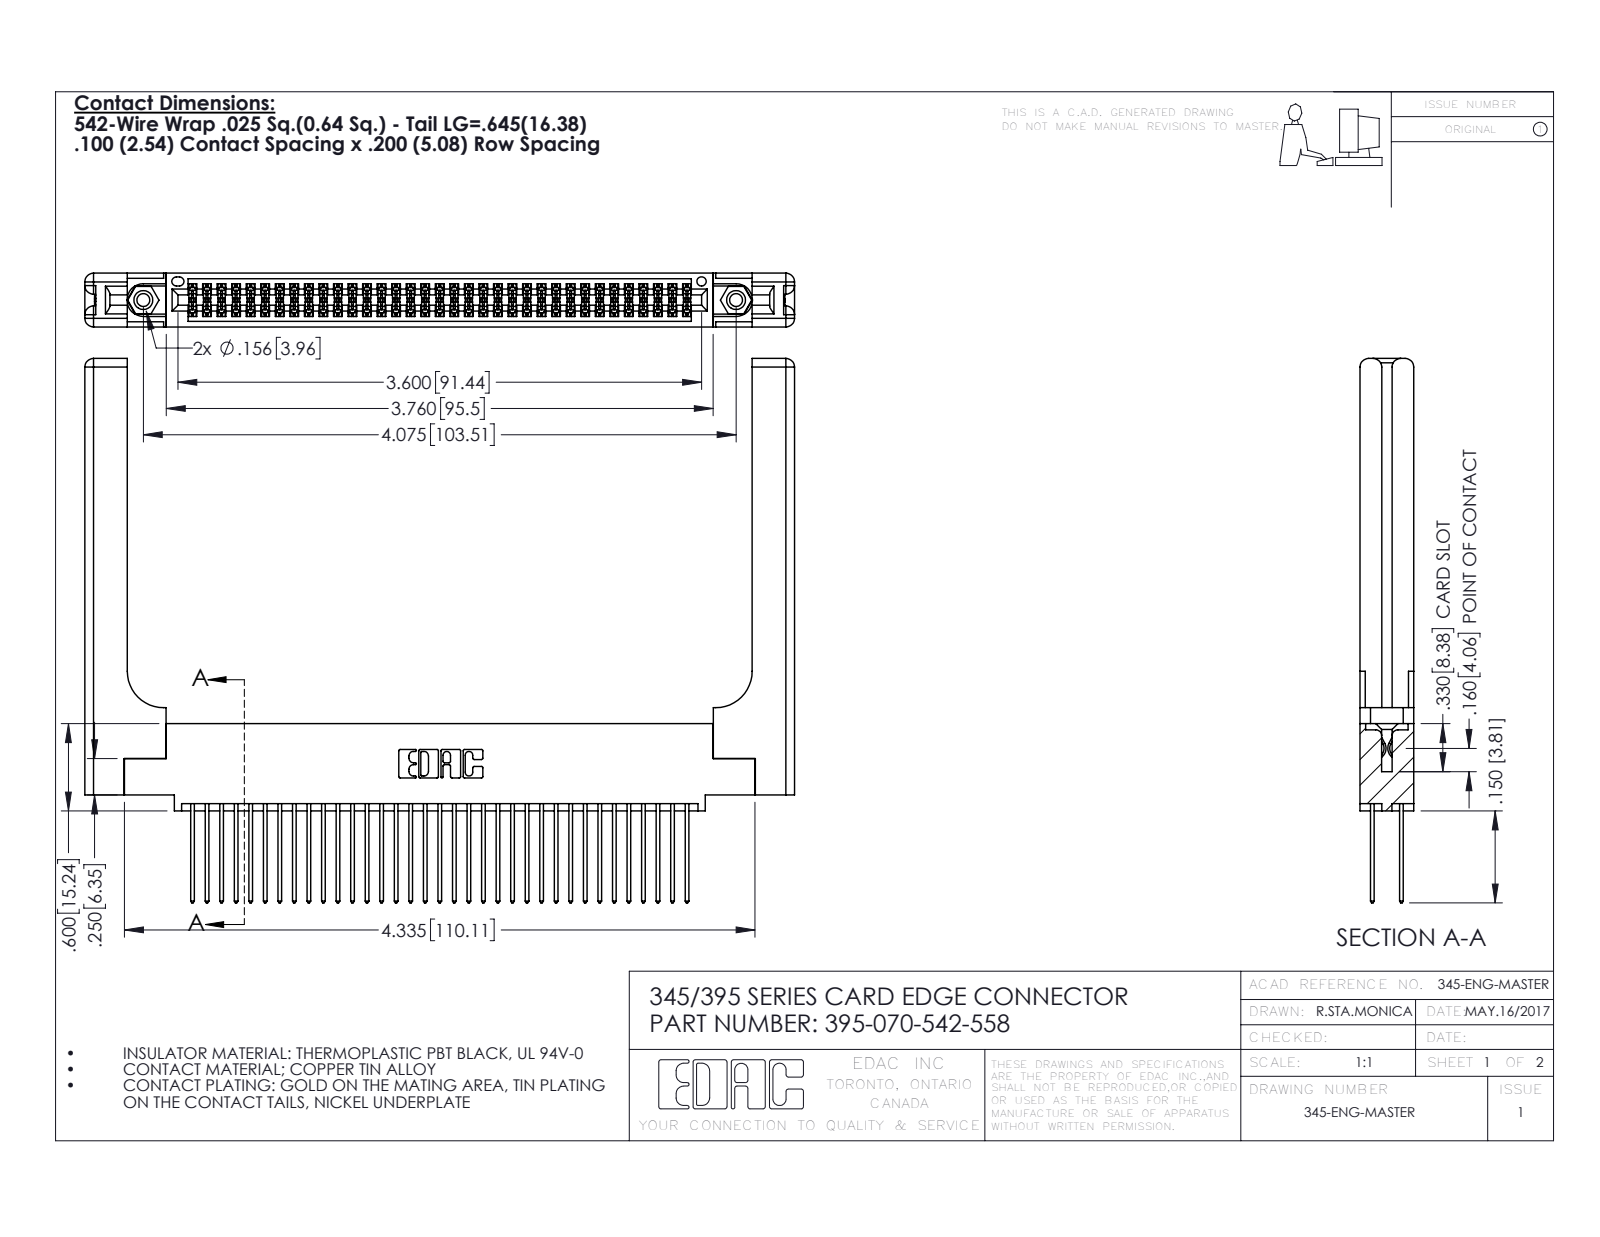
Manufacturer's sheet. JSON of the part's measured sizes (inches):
{"part_name": "345-292-001_345-293-142; 345 Part_0.110 Offset - 0.156 Dia-TH; 345-250-001_345-250-001-102; 345-220-058_345-220-058 (+1 more)", "step_written_by": "SolidWorks 2016 (CONFIG_CONTROL_DESIGN)", "units": "inches", "bodies": {"solids": 75, "faces": 3886, "planar": 2542, "cylindrical": 1284, "other": 60}, "overall_size": [4.879, 3.742, 0.37], "volume_in3": 1.263, "surface_area_in2": 38.15, "round_holes": [[0.089, 2], [0.125, 2], [0.156, 2], [0.064, 1]], "round_bosses_or_shafts": [[0.155, 2]], "partial_cylinders_radius": [[0.006, 105], [0.01, 70], [0.01, 22], [0.06, 16], [0.007, 6], [0.031, 6], [0.026, 3], [0.014, 2]], "face_to_face_distances": [0.072, 0.298, 0.37, 0.098, 0.272, 0.025, 0.2, 0.225, 0.175, 0.148], "hole_center_spacings": [0.27, 3.839, 4.075]}
